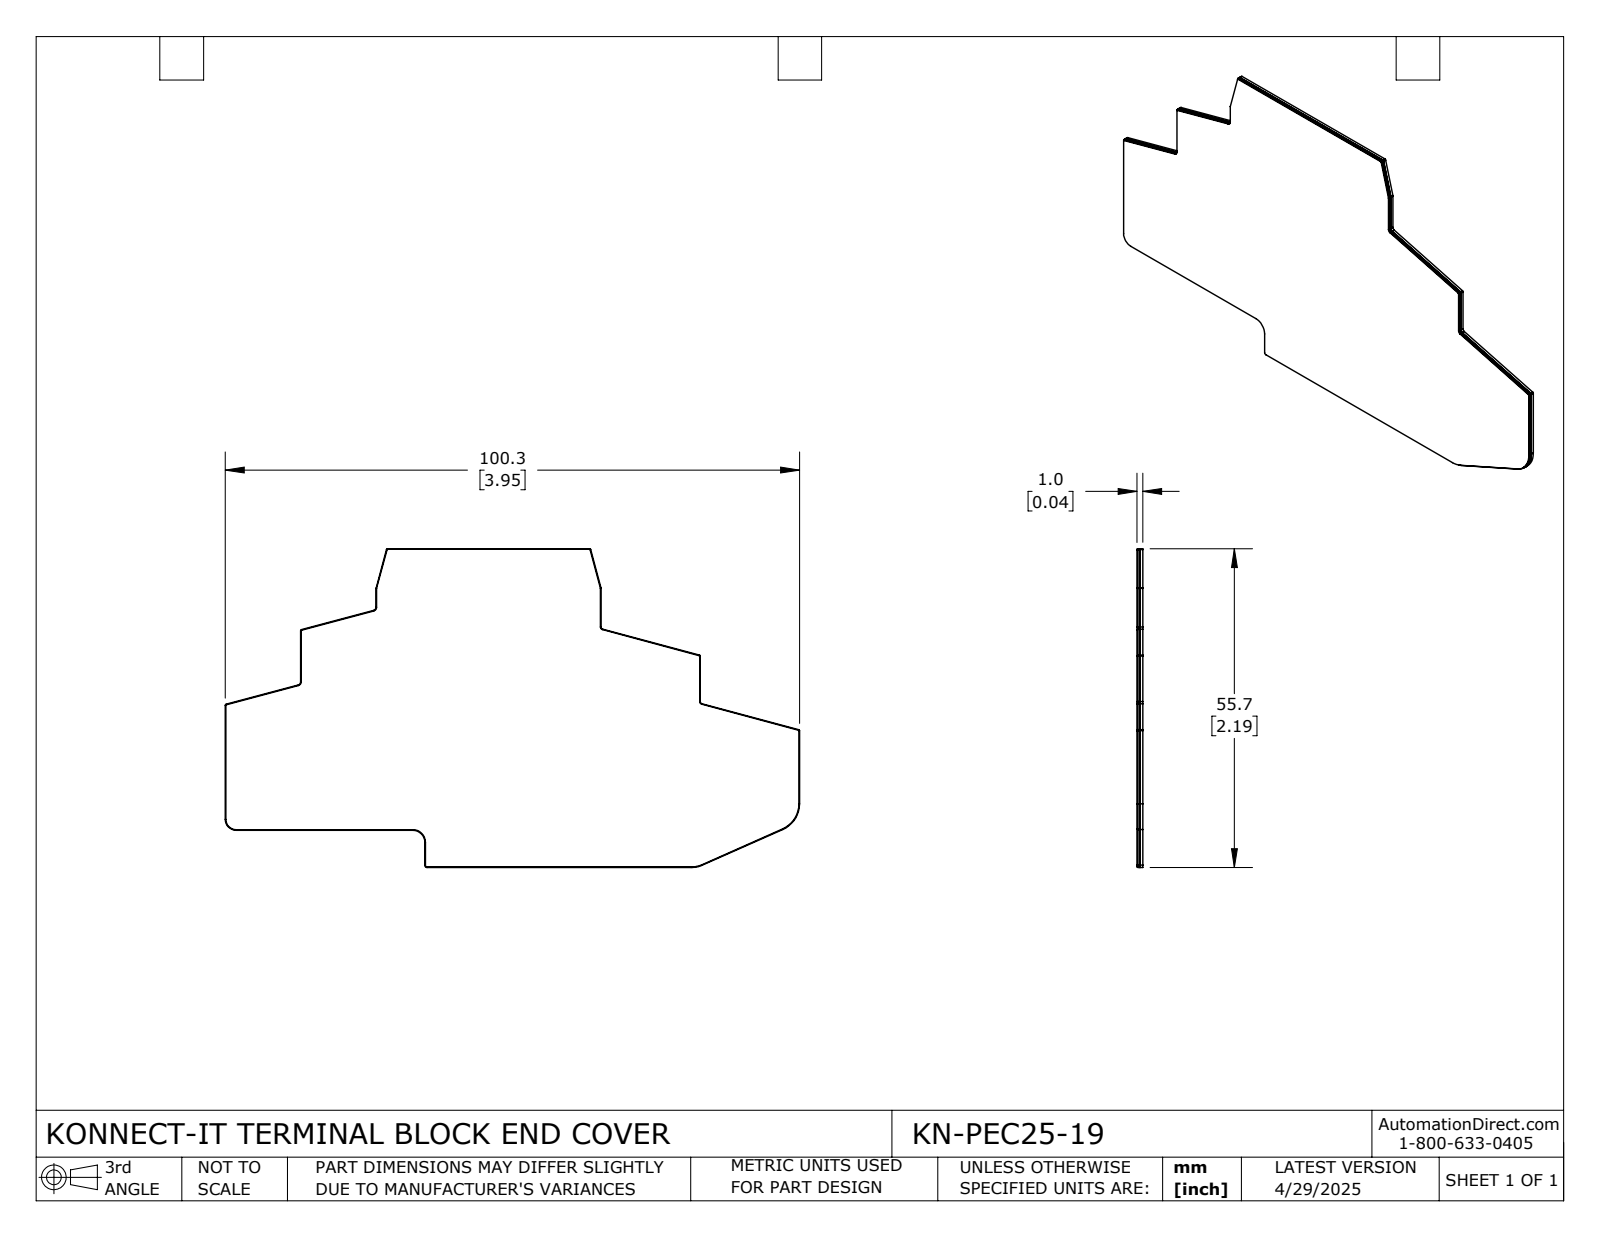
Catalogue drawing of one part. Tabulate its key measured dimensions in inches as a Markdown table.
| quantity | value |
| --- | --- |
| part name | KN-PEC25-19 |
| STEP written by | SolidWorks 2024 (CONFIG_CONTROL_DESIGN) |
| units | inches |
| bodies | 2 solids, 107 faces (56 planar, 51 cylindrical, 0 other) |
| overall size | 3.948 × 2.191 × 0.039 |
| volume | 0.243 in³ |
| surface area | 25.12 in² |
| partial cylindrical surfaces (radius × count) | 0.004 × 8, 0.008 × 8, 0.016 × 3, 0.02 × 2, 0.024 × 2, 0.028 × 2, 0.189 × 2, 0.193 × 2 |
| main face-to-face distances | 0.02, 0.039, 0.257, 2.191, 0.033, 0.014, 1.935, 0.319, 0.361, 2.187 |
